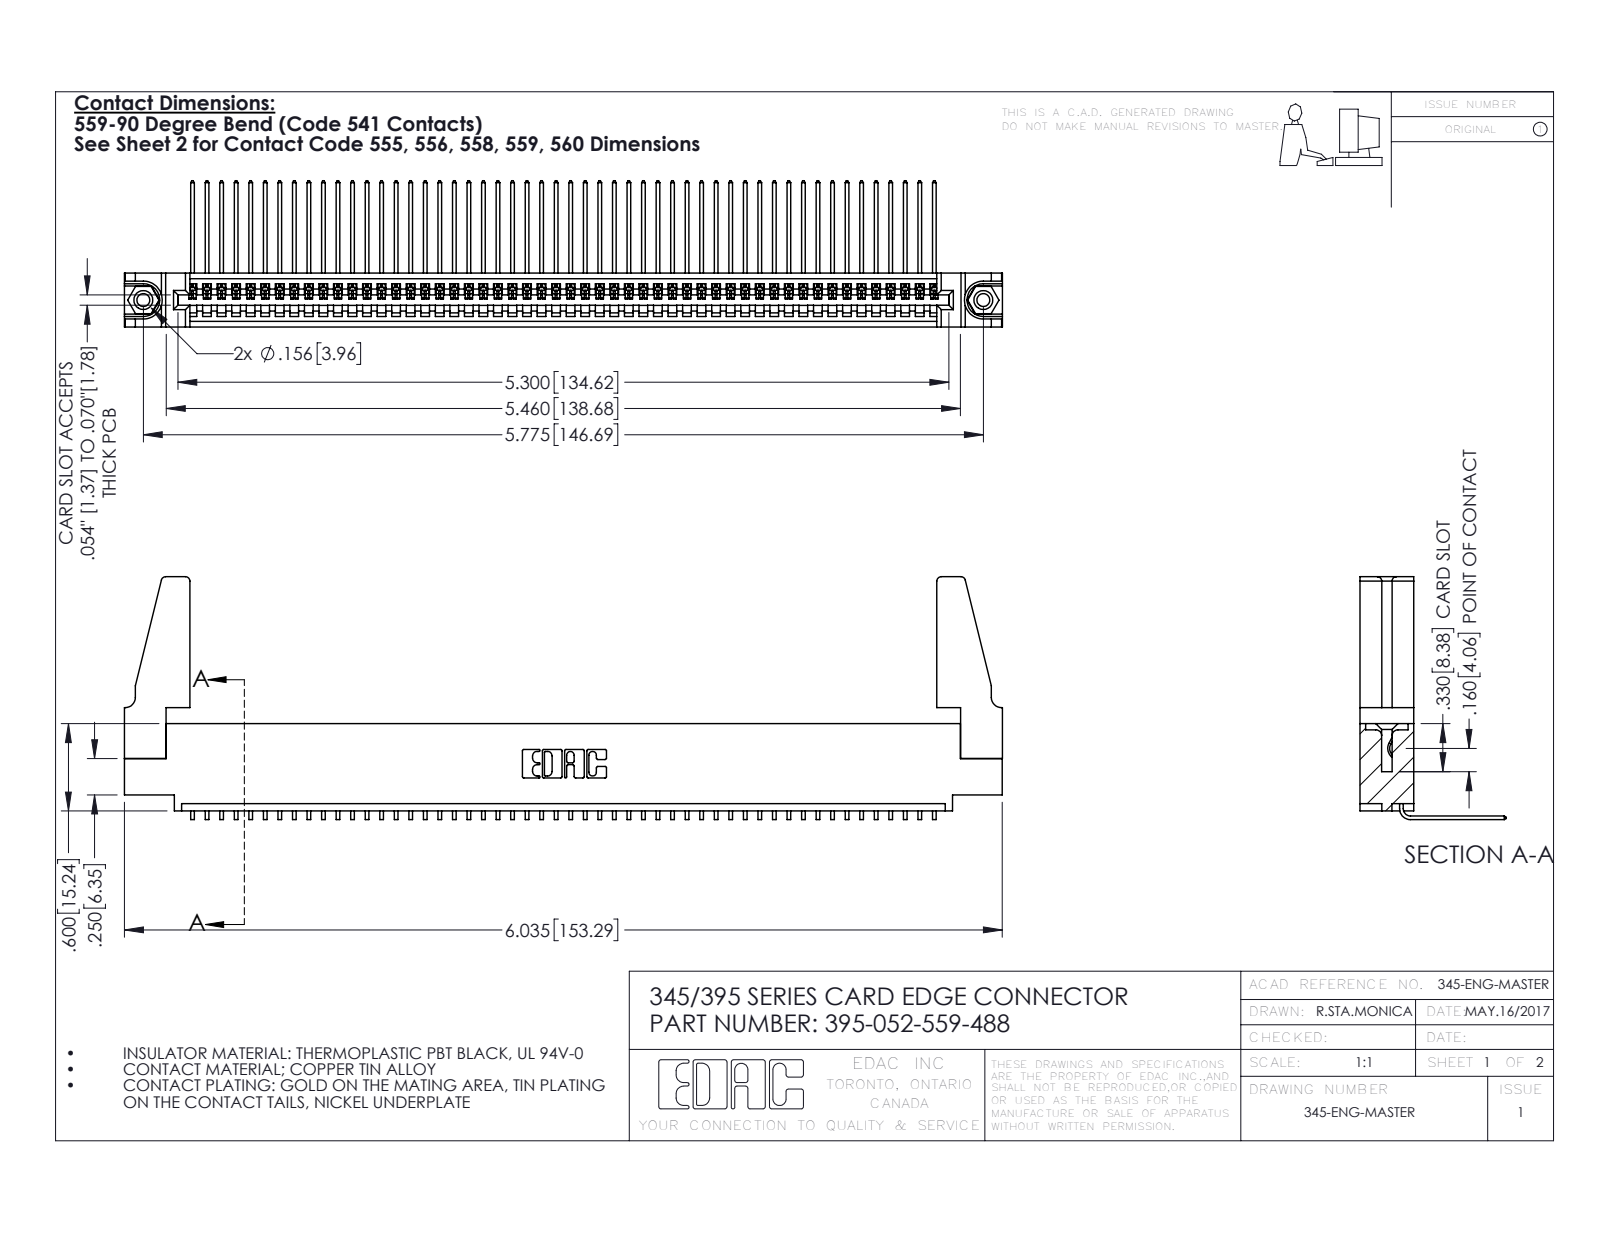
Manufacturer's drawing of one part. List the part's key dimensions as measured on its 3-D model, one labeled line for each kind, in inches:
Part name (STEP PRODUCT): 345-220-078_345-220-088; 345-292-001_558 559 Tail - 1; 395-052-559-488; 345-250-001_345-250-001-102 (+1 more)
STEP written by: SolidWorks 2016 (CONFIG_CONTROL_DESIGN)
Units: inches
Bodies: 57 solids, 3374 faces (2340 planar, 1018 cylindrical, 16 other)
Overall size (bounding box): 6.036 × 1.669 × 1.005
Volume: 1.098 in³ · Surface area: 37.14 in²
Round holes (diameter × count): ⌀0.089 ×2, ⌀0.125 ×2, ⌀0.156 ×2, ⌀0.064 ×1
Round bosses / shafts (diameter × count): ⌀0.155 ×2
Partial cylindrical surfaces — rounded edges, fillets, slot ends (radius × count): R0.006 ×104, R0.01 ×22, R0.03 ×8, R0.007 ×6, R0.031 ×6, R0.026 ×3, R0.031 ×2, R0.04 ×2
Main face-to-face distances: 0.072, 0.298, 0.37, 0.2, 0.098, 0.272, 0.025, 0.225, 0.149, 0.072
Hole centre spacings: 0.27, 5.539, 5.775
